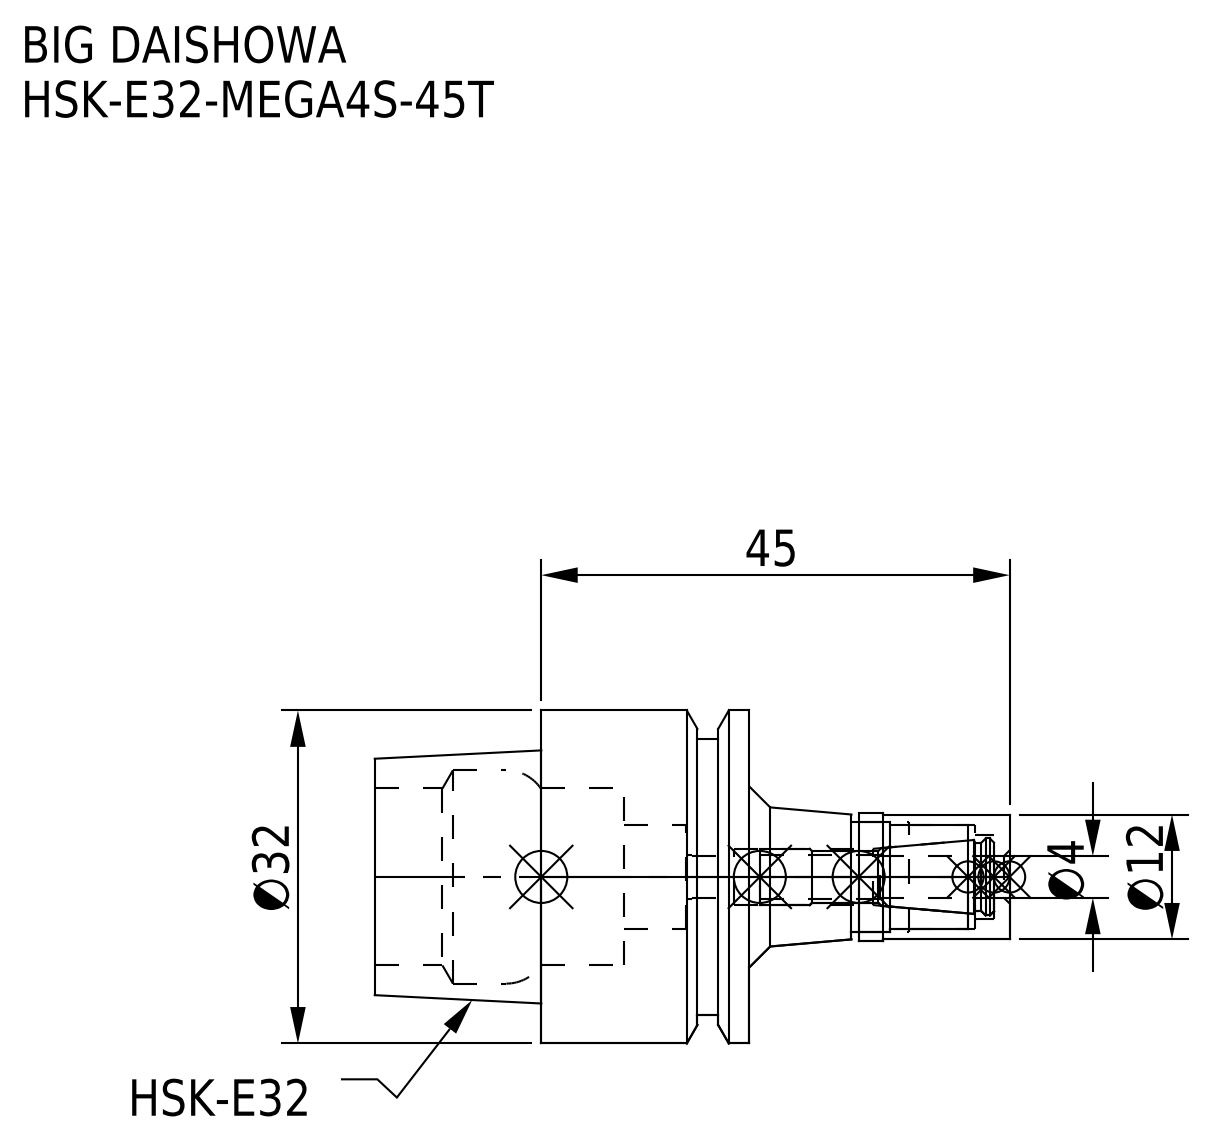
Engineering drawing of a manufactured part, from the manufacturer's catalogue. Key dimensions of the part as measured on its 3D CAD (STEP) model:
Part name (STEP PRODUCT): DXF_TEMP_ASSY_ASM_4_ASM.stp; HSK-E32-MEGA4S-45T-040.stp; MGN4S_1.stp; HSK-E32-MEGA4S-45T_1.stp (+3 more)
STEP written by: SolidWorks 2019 (CONFIG_CONTROL_DESIGN)
Units: millimetres
Bodies: 2 solids, 74 faces (18 planar, 38 cylindrical, 18 other)
Overall size (bounding box): 61 × 32 × 32
Volume: 17 884 mm³ · Surface area: 8 995 mm²
Round holes (diameter × count): ⌀4.1 ×1, ⌀4.2 ×1, ⌀5.4 ×1, ⌀8 ×1, ⌀10 ×1, ⌀10.5 ×1, ⌀17 ×1, ⌀20.5 ×1
Round bosses / shafts (diameter × count): ⌀32 ×1, ⌀26.5 ×1, ⌀12.3 ×1, ⌀12 ×1
Main face-to-face distances: 20, 16, 36, 12.05, 7.95, 23.95, 25, 3, 15, 37.05
